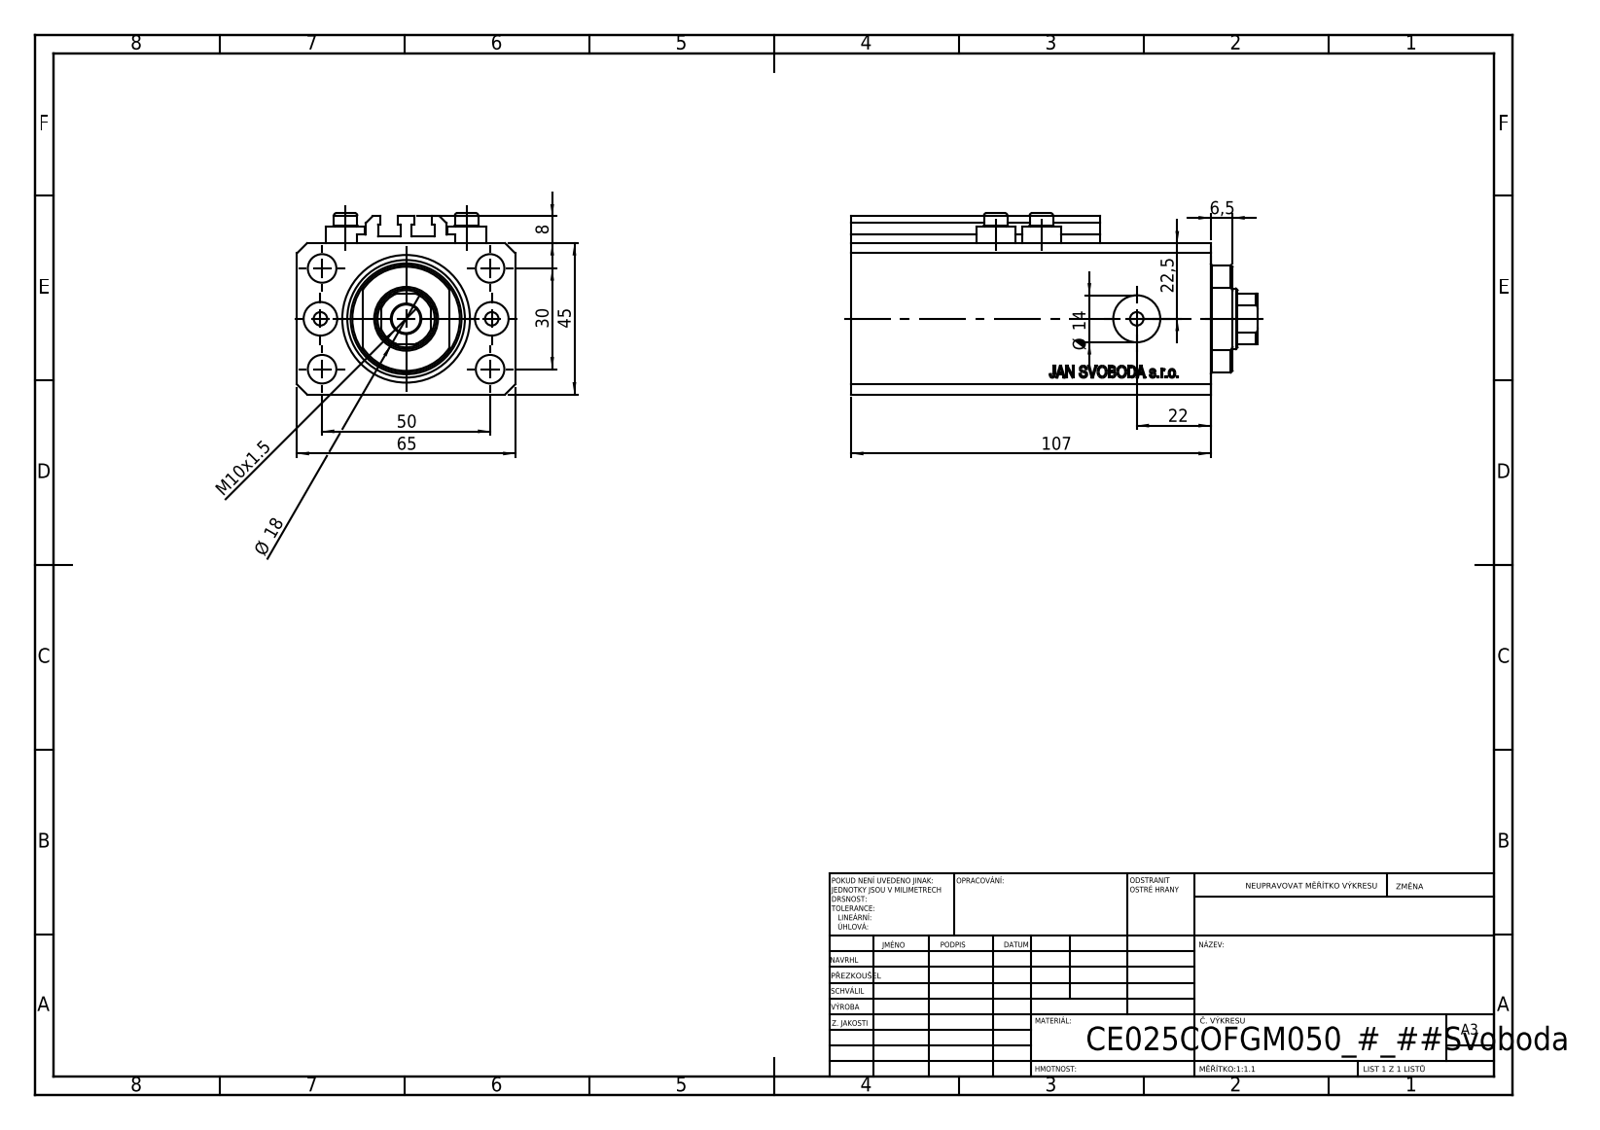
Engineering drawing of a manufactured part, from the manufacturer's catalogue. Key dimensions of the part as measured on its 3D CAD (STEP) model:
Part name (STEP PRODUCT): ALLEN BOLT V250CE; V250CE_C_Body; V250CE_VC_C; V250CE_C_VCP
STEP written by: SolidWorks 2019 (CONFIG_CONTROL_DESIGN)
Units: millimetres
Bodies: 8 solids, 1034 faces (504 planar, 86 cylindrical, 444 other)
Overall size (bounding box): 121 × 65 × 54
Volume: 289 033 mm³ · Surface area: 73 936 mm²
Round holes (diameter × count): ⌀4 ×8, ⌀8.5 ×5, ⌀10 ×2, ⌀14 ×2, ⌀18 ×1, ⌀25 ×1, ⌀38 ×1
Round bosses / shafts (diameter × count): ⌀11.6 ×4, ⌀7 ×4
Partial cylindrical surfaces — rounded edges, fillets, slot ends (radius × count): R0.2 ×10, R8.5 ×1, R16 ×1
Main face-to-face distances: 45, 65, 14, 93, 107, 47, 2.5, 20.5, 10, 2
Hole centre spacings: 15.01, 29.15, 52.68, 13.6, 25.5, 30, 36, 38.48
